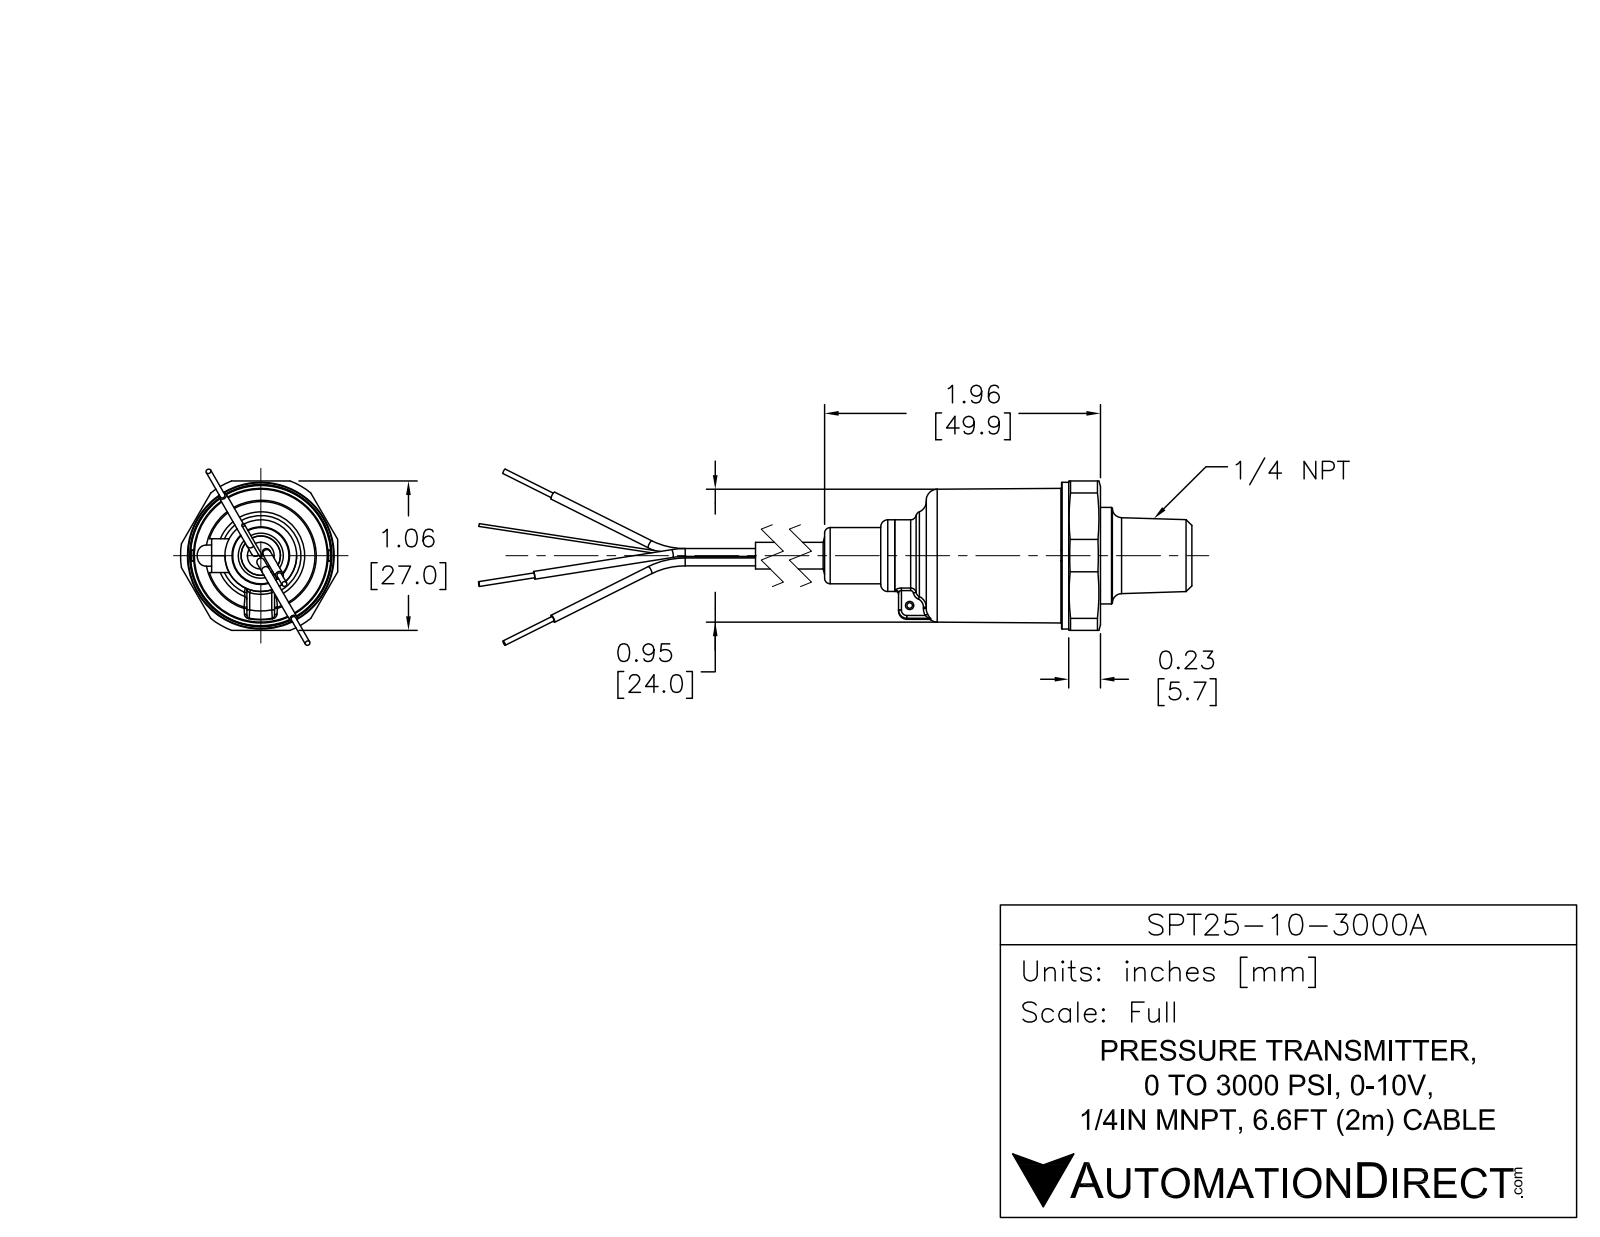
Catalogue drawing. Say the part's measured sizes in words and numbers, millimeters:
The part is named "SPT25-10-3000A". Its 3-D file was written by "SolidWorks 2017 (AUTOMOTIVE_DESIGN)". It is 7 solids with 116 faces: 32 planar, 49 cylindrical and 35 other. Overall it measures 153.3 by 29 by 27.09 millimeters. Its volume is 20 801 cubic millimeters and its surface area 7 170 square millimeters. Round holes: 1 of diameter 1, 1 of diameter 3.3. Round bosses or shafts: 6 of diameter 1.4, 5 of diameter 0.75, 1 of diameter 26.75, 1 of diameter 24, 1 of diameter 17.5, 1 of diameter 14, 1 of diameter 13, 1 of diameter 10. Partial cylindrical surfaces (rounded edges, fillets, slot ends): 1 of radius 2, 1 of radius 14.5. The main face-to-face distances are 6.75, 24, 17.25, 42.75, 49.5, 66.75, 44, 1.25, 5.5, 22.75.
